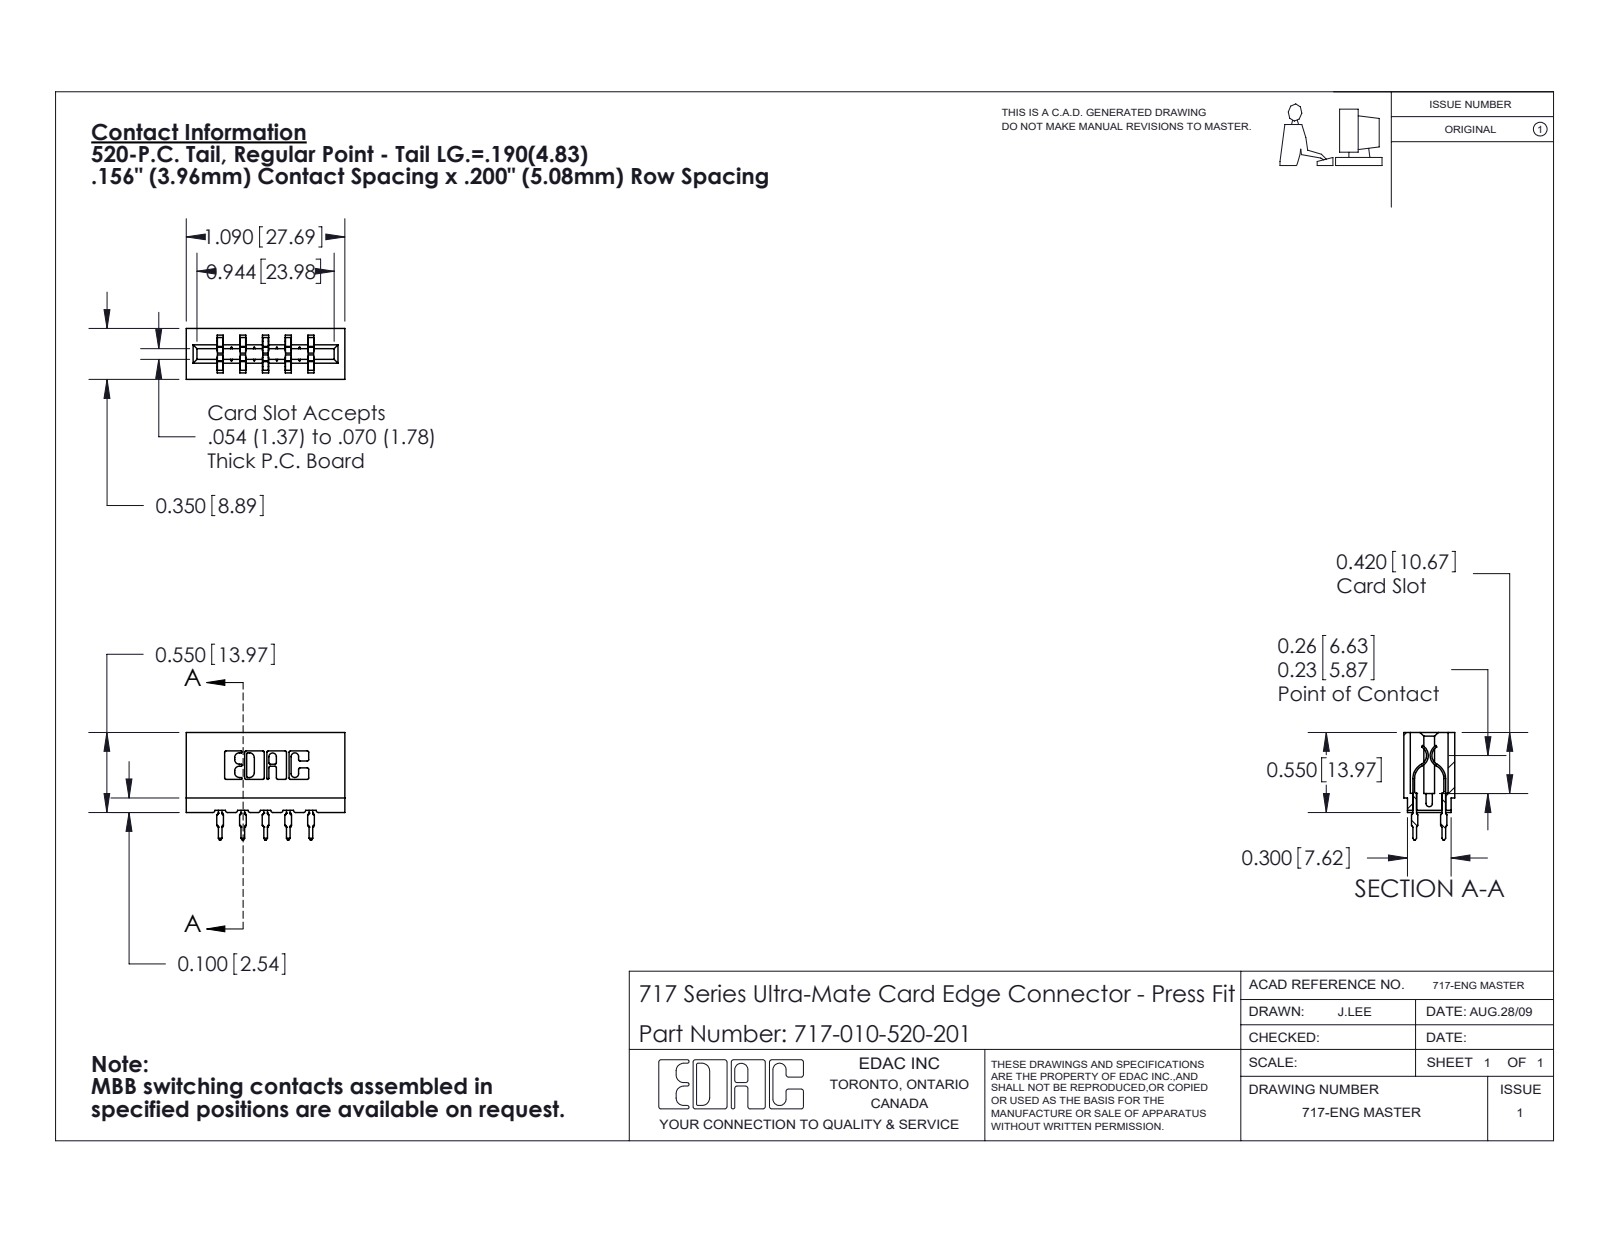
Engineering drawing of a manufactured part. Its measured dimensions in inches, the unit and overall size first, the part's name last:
Units: inches
Overall size (bounding box): 1.09 × 0.739 × 0.35
Partial cylindrical surfaces — rounded edges, fillets, slot ends (radius × count): R0.01 ×22, R0.021 ×20, R0.015 ×10, R0.005 ×8, R0.011 ×8, R0.007 ×6, R0.031 ×6, R0.026 ×3
Main face-to-face distances: 0.212, 0.156, 0.138, 0.35, 0.198, 0.042, 0.312, 0.312, 0.468, 0.074
Volume: 0.155 in³ · Surface area: 5.182 in²
Bodies: 11 solids, 994 faces (519 planar, 215 cylindrical, 260 other)
Part name (STEP PRODUCT): 745-292-001_520; 717-010-520-201; 717 Part_Insulator Option - 06
STEP written by: SolidWorks 2020 (CONFIG_CONTROL_DESIGN)
